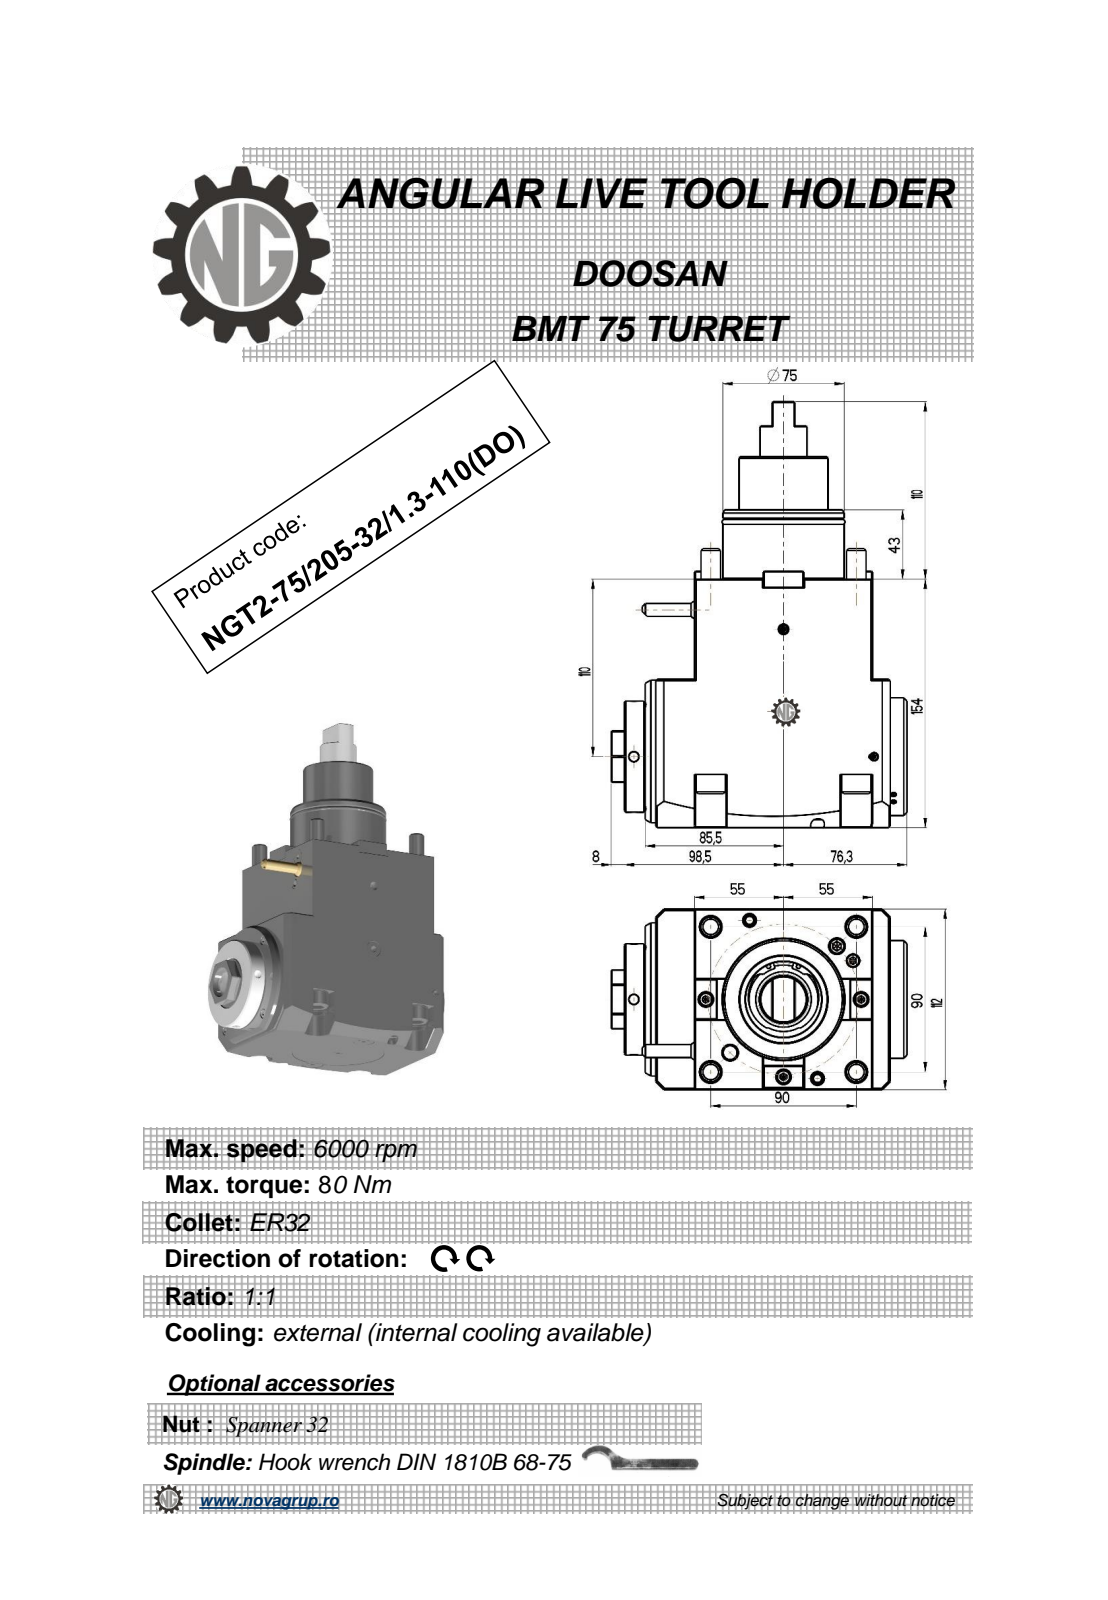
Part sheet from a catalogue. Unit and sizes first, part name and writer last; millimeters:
Units: millimetres
Overall size (bounding box): 264 × 182.8 × 112
Round holes (diameter × count): ⌀6 ×2, ⌀8.5 ×2, ⌀3 ×1, ⌀5 ×1, ⌀23 ×1
Round bosses / shafts (diameter × count): ⌀18 ×4, ⌀12 ×4, ⌀95 ×1, ⌀75 ×1, ⌀74 ×1, ⌀73 ×1, ⌀70 ×1, ⌀69 ×1
Partial cylindrical surfaces — rounded edges, fillets, slot ends (radius × count): R9.5 ×4, R0.8 ×2, R350 ×2
Main face-to-face distances: 112, 110, 154, 121, 11, 62, 43.5, 92, 30.5, 131.3
Hole centre spacings: 68.04, 93.34, 96.46, 129.77
Volume: 2 643 000 mm³ · Surface area: 148 353 mm²
Bodies: 2 solids, 292 faces (146 planar, 69 cylindrical, 77 other)
Part name (STEP PRODUCT): NGT2_75_205_32_1_3_110_DO
STEP written by: PRO/ENGINEER BY PARAMETRIC TECHNOLOGY CORPORATION, 2010280 (CONFIG_CONTROL_DESIGN)
